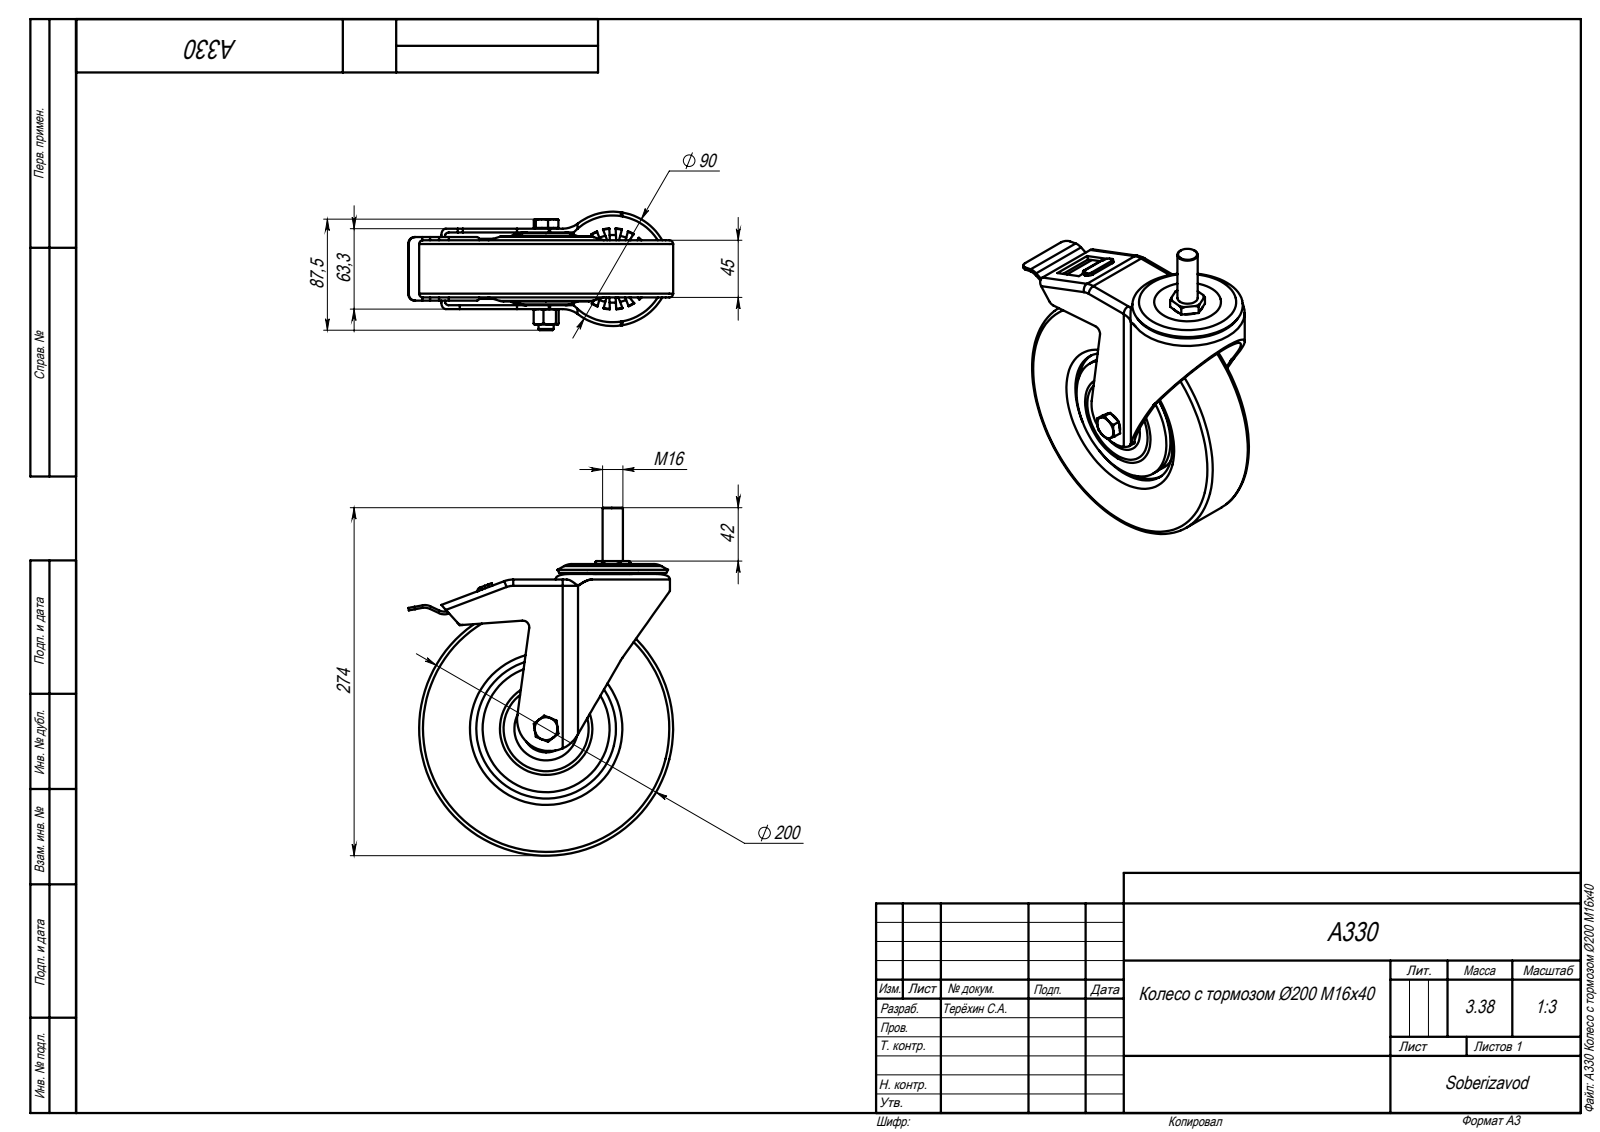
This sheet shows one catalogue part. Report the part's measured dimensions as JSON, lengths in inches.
{"part_name": "Колесо_00; A330 Колесо с тормозом O200 М16х40; hex bolt gradeab_din_DIN EN 24014 - M12 x 80 x 30-N; Болт_00 (+6 more)", "step_written_by": "SolidWorks 2018 (AUTOMOTIVE_DESIGN)", "units": "inches", "bodies": {"solids": 10, "faces": 408, "planar": 185, "cylindrical": 77, "other": 146}, "overall_size": [10.786, 8.207, 4.986], "volume_in3": 83.66, "surface_area_in2": 379.1, "round_holes": [[0.472, 2], [0.315, 1], [0.402, 1], [3.78, 1], [4.331, 1]], "round_bosses_or_shafts": [[7.874, 1], [3.937, 1], [0.709, 1], [0.63, 1]], "partial_cylinders_radius": [[0.197, 10], [0.118, 5], [0.394, 4], [0.787, 3], [0.984, 3], [0.079, 2], [1.654, 1], [1.772, 1]], "face_to_face_distances": [0.118, 1.772, 0.512, 1.26, 0.242, 0.754, 1.502, 2.014, 0.36, 0.872]}
